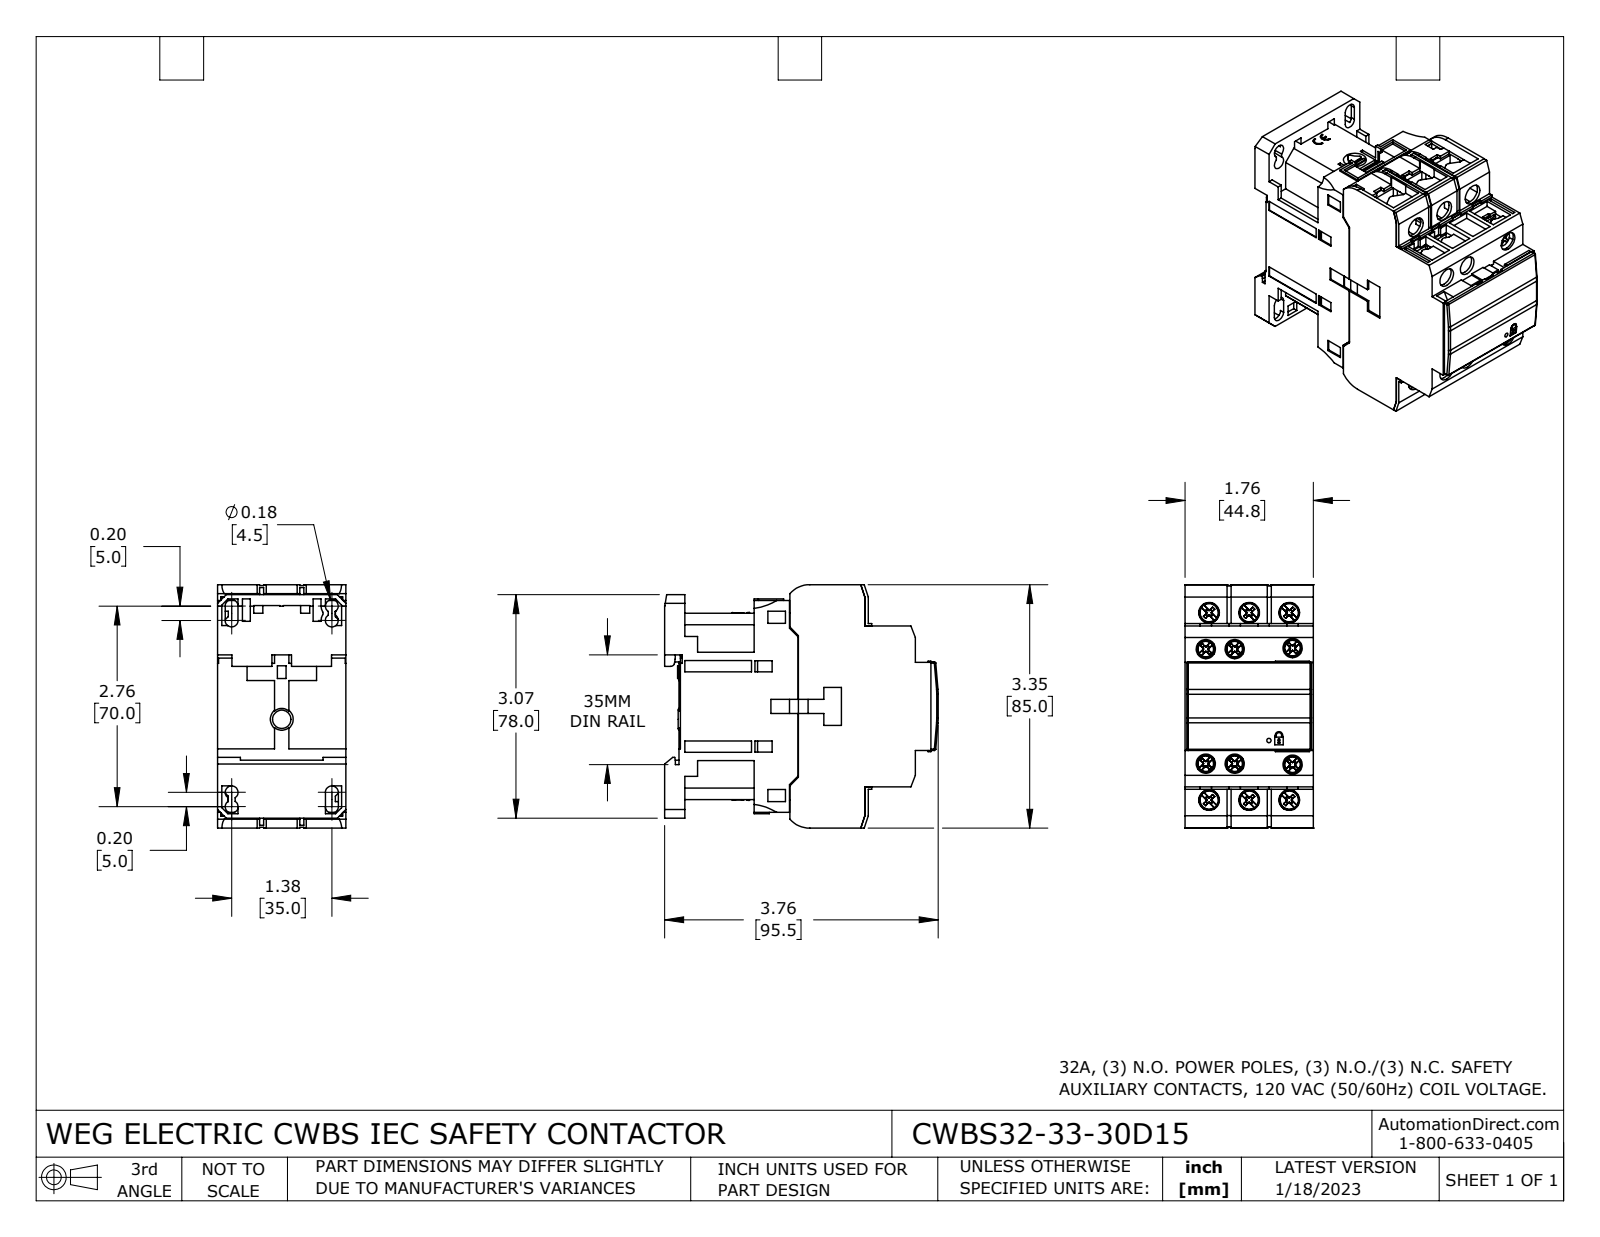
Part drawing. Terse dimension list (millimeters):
name: CWBS32-33-30D15
written by: SolidWorks 2021 (CONFIG_CONTROL_DESIGN)
unit: mm
bodies: 42 solids, 2461 faces (1808 planar, 446 cylindrical, 207 other)
size: 95.5 × 85 × 44.8
volume: 237 400 mm³; area: 70 190 mm²
holes: 6× ⌀3.1, 6× ⌀3.6, 6× ⌀6.7, 6× ⌀7.2, 4× ⌀4.5, 1× ⌀1.5
bosses: 6× ⌀5.1, 6× ⌀4.3, 6× ⌀4, 6× ⌀3.5, 4× ⌀2.7, 2× ⌀2.7
rounds: 42× R0.5, 24× R0.7, 12× R1.8, 12× R2.1, 12× R24.5, 12× R27.4, 12× R54.1, 12× R79.4
face distances: 44.8, 1.2, 43, 3.4, 46.3, 0.6, 5.5, 87.5, 7, 43.6
hole spacings: 14, 66.9, 65.4, 4.2, 4.4, 5, 10.1, 12.4
